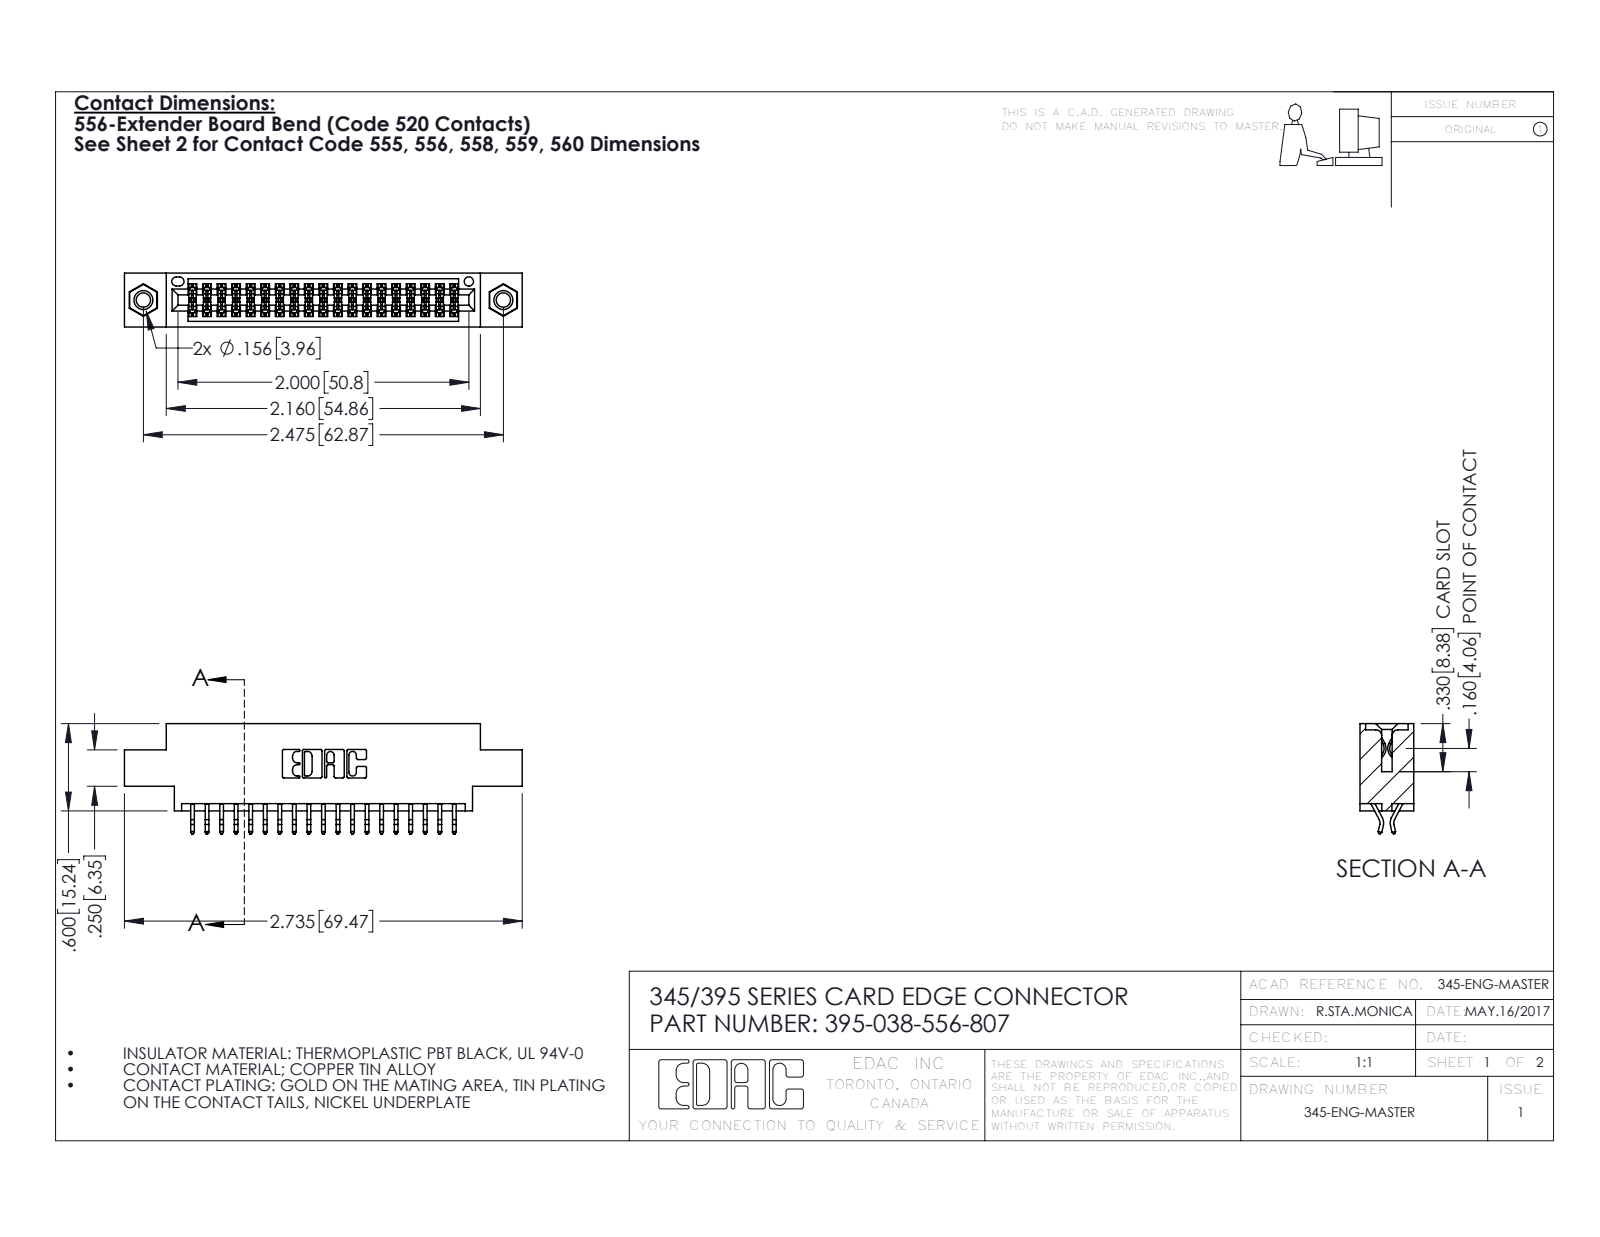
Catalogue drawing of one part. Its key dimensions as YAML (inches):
part_name: "345-250-001_345-250-005-103; 395-038-556-807; 345 Part_0.170 Offset - 0.156 Dia-TI; 345-292-001_556 Tail"
step_written_by: "SolidWorks 2016 (CONFIG_CONTROL_DESIGN)"
units: inches
bodies: {solids: 41, faces: 2318, planar: 1522, cylindrical: 780, other: 16}
overall_size: [2.735, 0.757, 0.37]
volume: 0.391
surface_area: 14.2
round_holes:
  - {diameter: 0.098, count: 2}
  - {diameter: 0.125, count: 2}
  - {diameter: 0.156, count: 2}
  - {diameter: 0.064, count: 1}
round_bosses_or_shafts:
  - {diameter: 0.155, count: 2}
partial_cylinders:
  - {radius: 0.006, count: 57}
  - {radius: 0.01, count: 22}
  - {radius: 0.007, count: 6}
  - {radius: 0.031, count: 6}
  - {radius: 0.026, count: 3}
  - {radius: 0.01, count: 2}
  - {radius: 0.014, count: 2}
  - {radius: 0.019, count: 2}
face_to_face_distances: [0.072, 0.298, 0.37, 0.2, 0.025, 0.098, 0.272, 0.225, 0.175, 0.1]
hole_center_spacings: [0.27, 2.241, 2.475]
